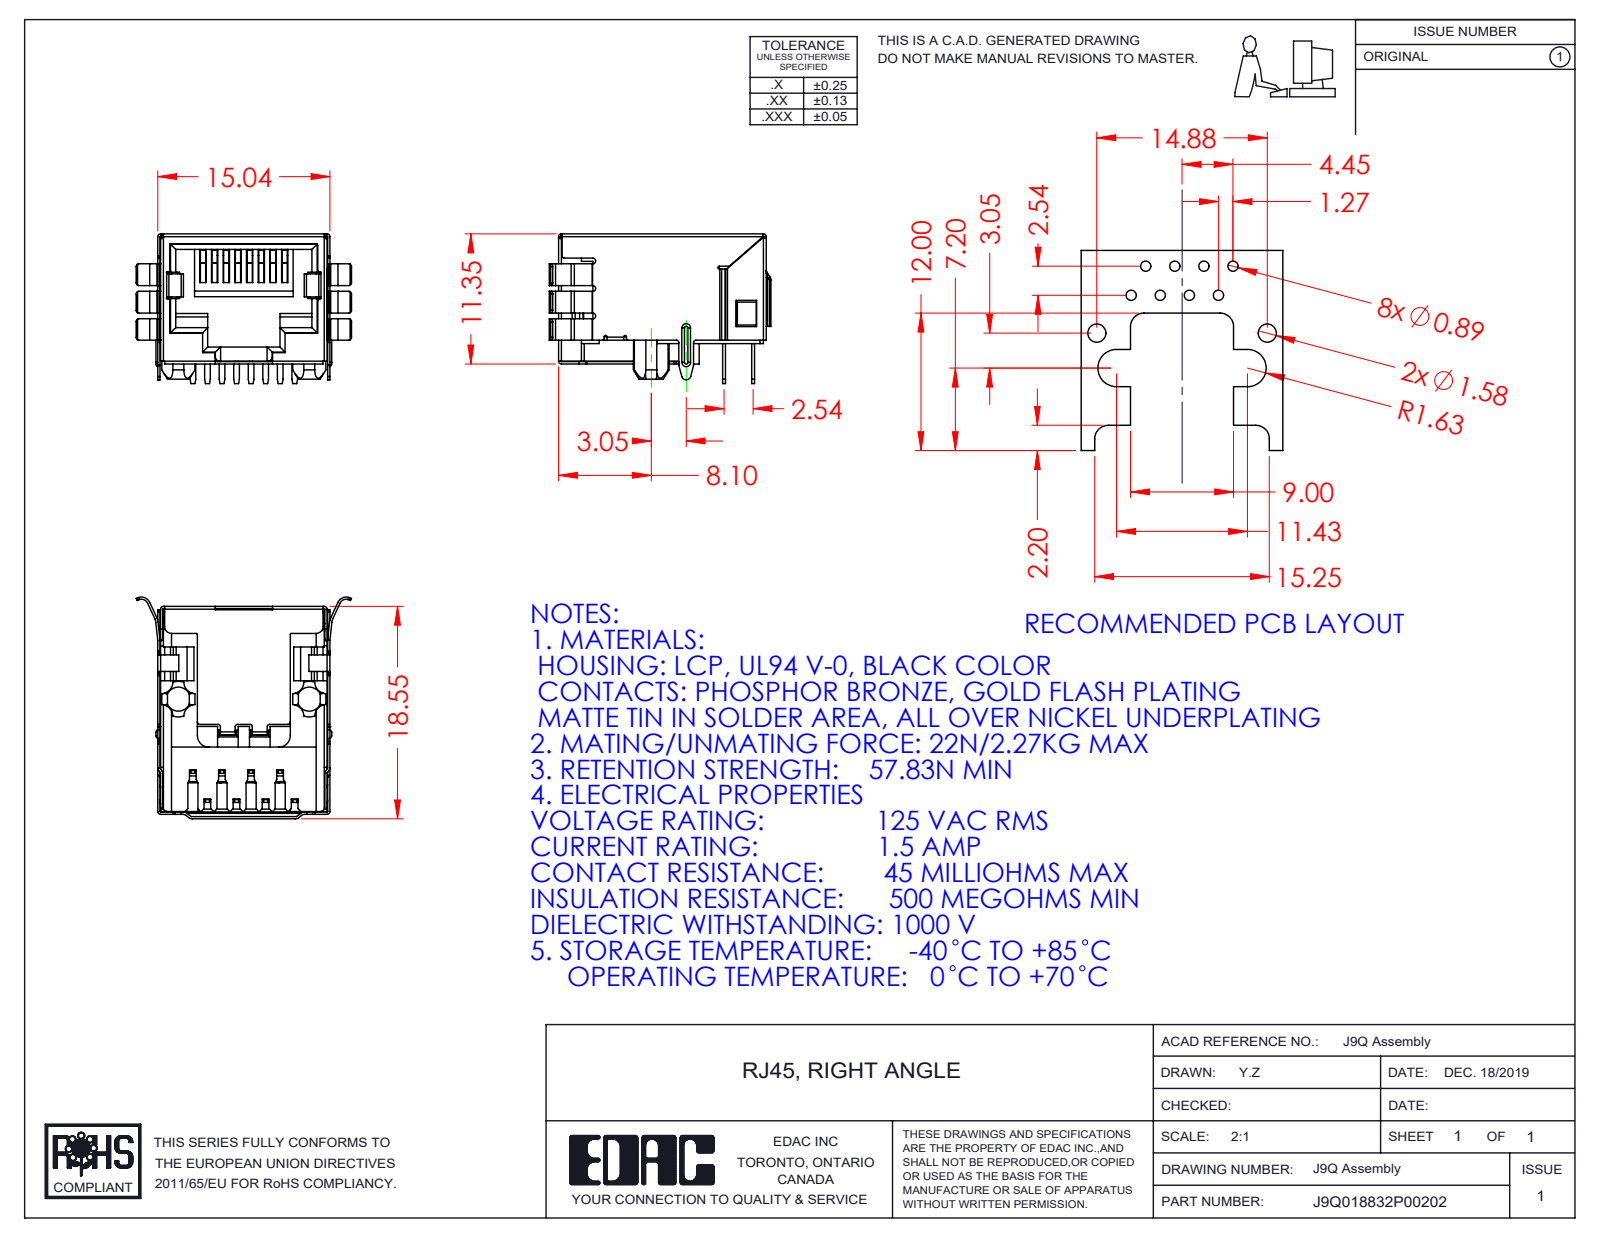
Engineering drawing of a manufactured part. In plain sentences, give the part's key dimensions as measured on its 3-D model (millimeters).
The part is named "9Q Contact Lock; 9Q Contacts; 9Q Insulator; J9Q018832P00202 (+1 more)". Its 3-D file was written by "SolidWorks 2016 (CONFIG_CONTROL_DESIGN)". It is 11 solids with 1339 faces: 949 planar, 369 cylindrical and 21 other. Overall it measures 19.36 by 18.81 by 13.07 millimeters. Its volume is 1 193 cubic millimeters and its surface area 4 818 square millimeters. Partial cylindrical surfaces (rounded edges, fillets, slot ends): 43 of radius 0.1, 35 of radius 0.2, 34 of radius 0.25, 24 of radius 0.15, 19 of radius 0.5, 14 of radius 0.3, 8 of radius 0.6, 8 of radius 1.05. The main face-to-face distances are 14.59, 14.54, 14.84, 14.34, 14.79, 0.5, 11.15, 14.29, 14.64, 15.04.
